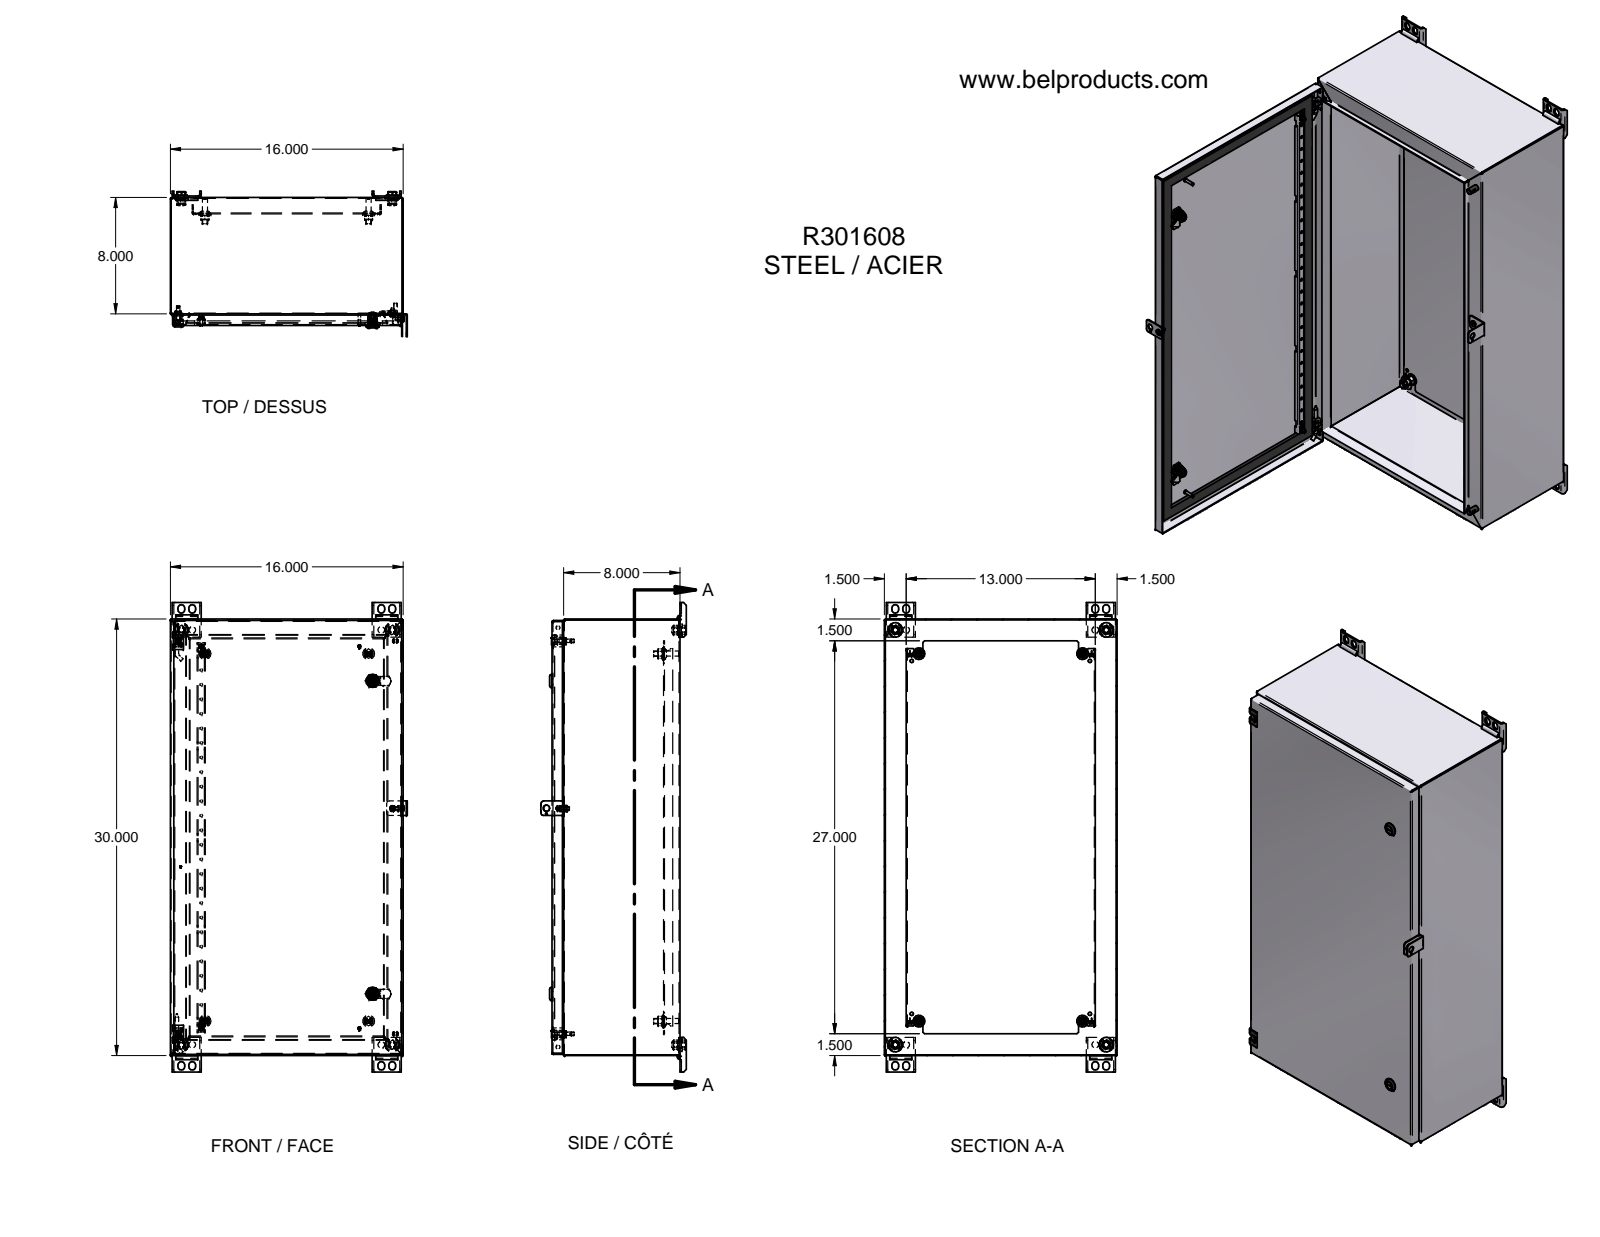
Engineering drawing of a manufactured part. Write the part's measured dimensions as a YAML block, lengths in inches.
part_name: "LOCK AVEC TOURNEVIS TYPE 4-12 SANS CAME; HOSING-oa0; INSERT POUR TOURNEVIS-oa1; NOIX DE FIXATION-oa2 (+8 more)"
step_written_by: "Unknown (AUTOMOTIVE_DESIGN)"
units: inches
bodies: {solids: 88, faces: 3592, planar: 2052, cylindrical: 640, other: 900}
overall_size: [32.266, 16.282, 9.995]
volume: 166
surface_area: 4941
round_holes:
  - {diameter: 0.184, count: 26}
  - {diameter: 0.125, count: 10}
  - {diameter: 0.375, count: 8}
  - {diameter: 0.406, count: 8}
  - {diameter: 0.456, count: 8}
  - {diameter: 0.014, count: 6}
  - {diameter: 0.159, count: 4}
  - {diameter: 0.236, count: 4}
  - {diameter: 0.265, count: 4}
  - {diameter: 0.355, count: 4}
  - {diameter: 0.415, count: 4}
  - {diameter: 0.5, count: 4}
round_bosses_or_shafts:
  - {diameter: 0.119, count: 10}
  - {diameter: 0.812, count: 8}
  - {diameter: 0.19, count: 5}
  - {diameter: 0.637, count: 4}
  - {diameter: 0.353, count: 4}
  - {diameter: 0.256, count: 4}
  - {diameter: 0.031, count: 4}
  - {diameter: 0.02, count: 4}
partial_cylinders:
  - {radius: 0.008, count: 84}
  - {radius: 0.032, count: 26}
  - {radius: 0.375, count: 22}
  - {radius: 0.012, count: 18}
  - {radius: 0.092, count: 18}
  - {radius: 0.01, count: 16}
  - {radius: 0.228, count: 16}
  - {radius: 0.187, count: 12}
face_to_face_distances: [0.06, 8.731, 8.672, 15.94, 8.791, 0.075, 7.6, 7.66, 1.071, 1.131]
hole_center_spacings: [0.515, 0.625, 0.75, 0.781, 1.225, 1.5, 1.644, 1.845]
